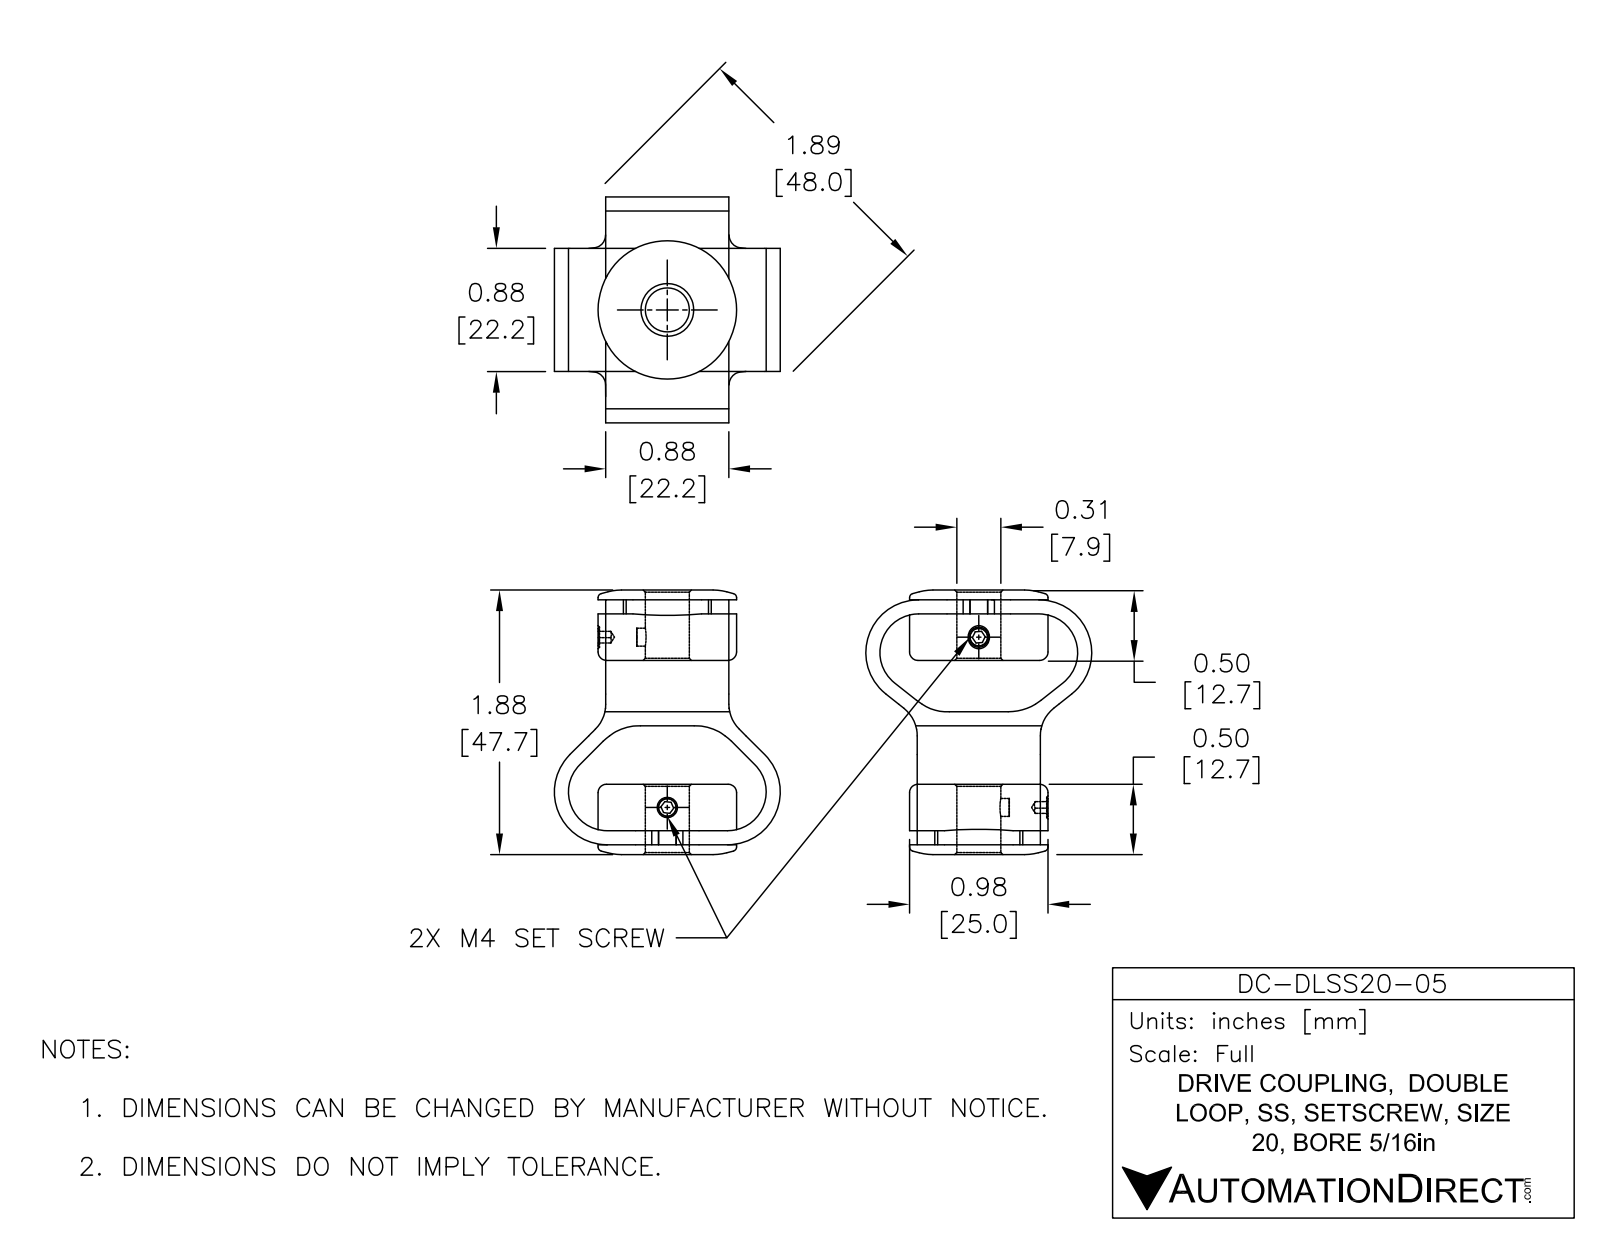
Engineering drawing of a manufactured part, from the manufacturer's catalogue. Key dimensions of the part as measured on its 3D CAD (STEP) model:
Part name (STEP PRODUCT): DC-DLSS20-05
STEP written by: SolidWorks 2015 (AUTOMOTIVE_DESIGN)
Units: millimetres
Bodies: 1 solid, 173 faces (90 planar, 47 cylindrical, 36 other)
Overall size (bounding box): 47.75 × 40.77 × 40.77
Volume: 18 183 mm³ · Surface area: 11 303 mm²
Round holes (diameter × count): ⌀3.24 ×2, ⌀7.94 ×1
Round bosses / shafts (diameter × count): ⌀25 ×1
Partial cylindrical surfaces — rounded edges, fillets, slot ends (radius × count): R9.53 ×7, R6.35 ×6, R6.99 ×4, R1.91 ×3, R1.91 ×1, R7.94 ×1
Main face-to-face distances: 2.54, 12.7, 35.05, 22.35, 13.08, 9.27, 1.78, 45.97, 10.92, 33.27
